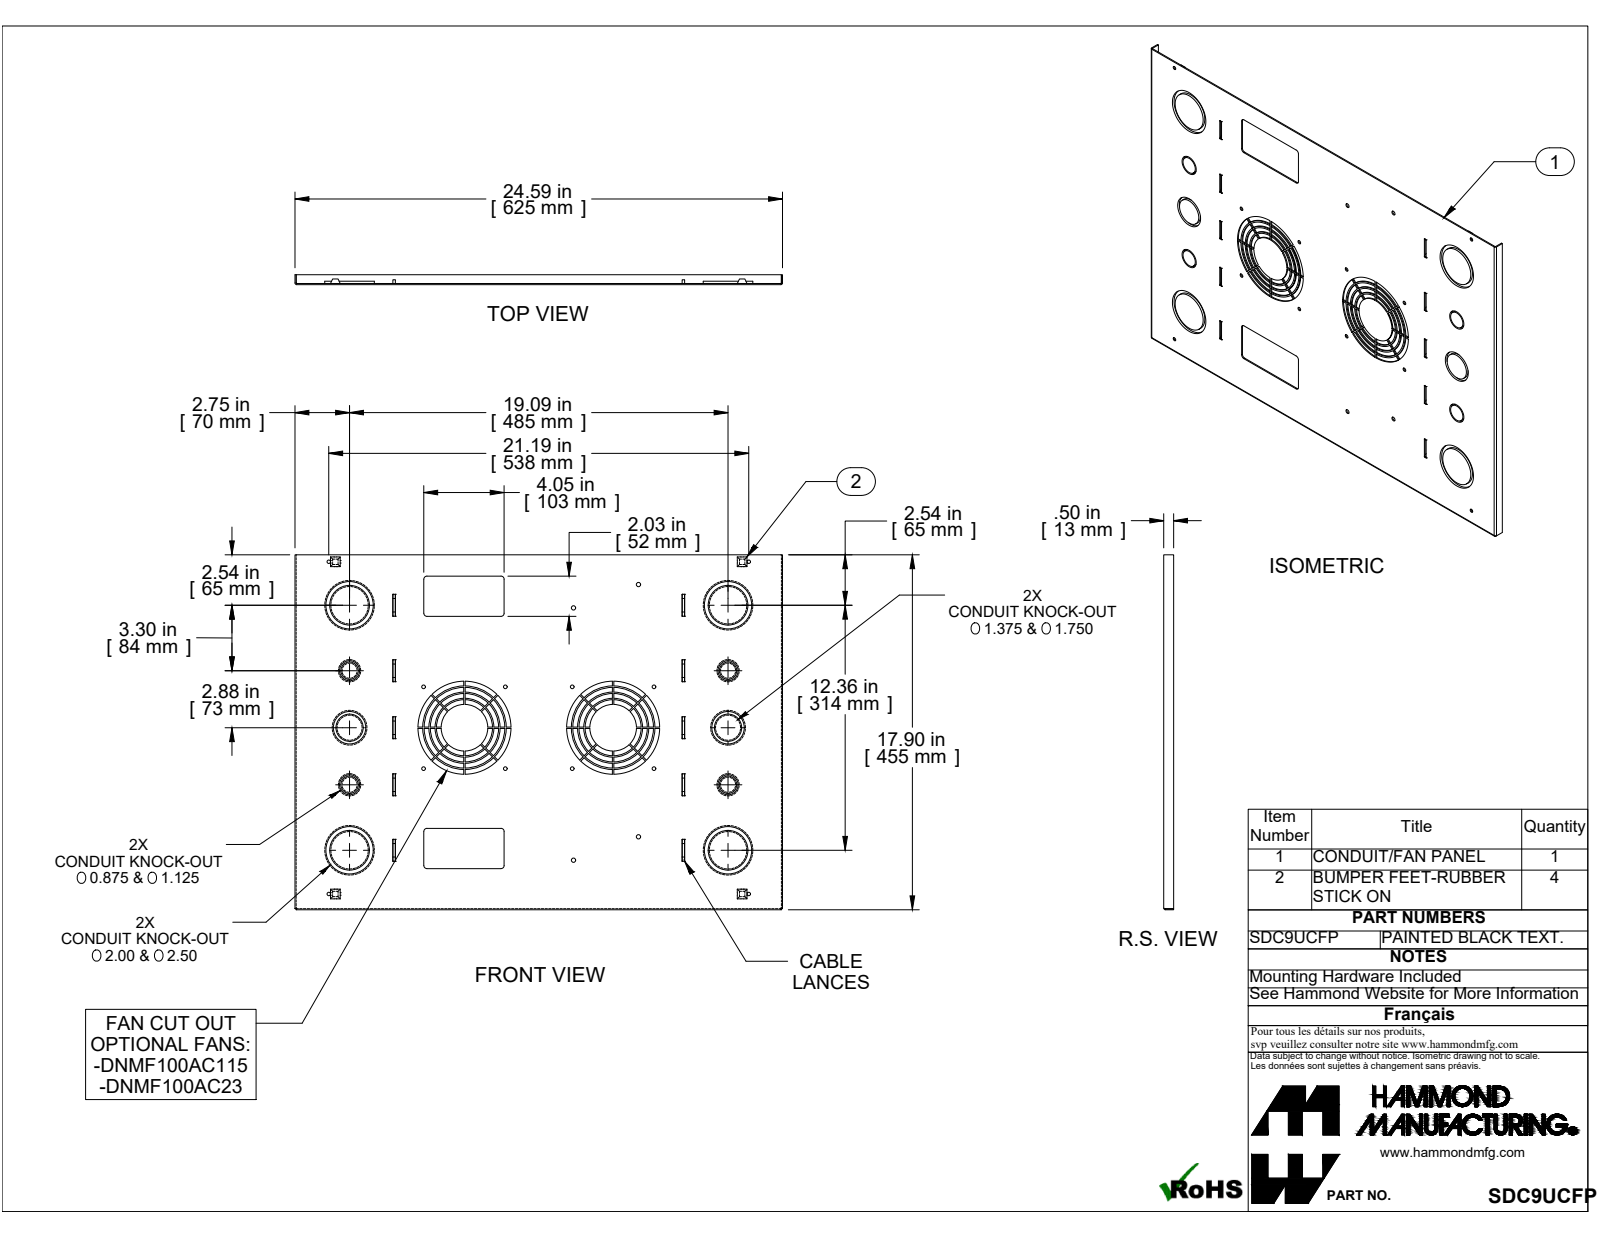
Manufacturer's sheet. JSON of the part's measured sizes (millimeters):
{"part_name": "SDC9UCFP", "step_written_by": "SolidWorks 2019 (CONFIG_CONTROL_DESIGN)", "units": "millimeters", "bodies": {"solids": 5, "faces": 646, "planar": 404, "cylindrical": 238, "other": 4}, "overall_size": [624.7, 454.7, 12.7], "volume_mm3": 413400, "surface_area_mm2": 583200, "round_holes": [[4.8, 8], [4.5, 4], [5.5, 4], [19.3, 4], [25.7, 4], [47.9, 4], [60.6, 4], [32, 2], [41.6, 2], [71.8, 2], [87.6, 2], [103.4, 2]], "round_bosses_or_shafts": [[63.5, 4], [50.8, 4], [22.2, 4], [107, 2], [91.3, 2], [75.5, 2], [59.7, 2], [44.5, 2]], "partial_cylinders_radius": [[1.4, 20], [4, 8], [0.7, 3], [2.2, 3]], "face_to_face_distances": [1.4, 3, 1.4, 623.2, 4.4, 621.8, 624.7, 1.5, 12.7, 11.3], "hole_center_spacings": [190.5, 485, 74.1, 74.1, 83.9, 97.1, 104.8, 104.8]}
